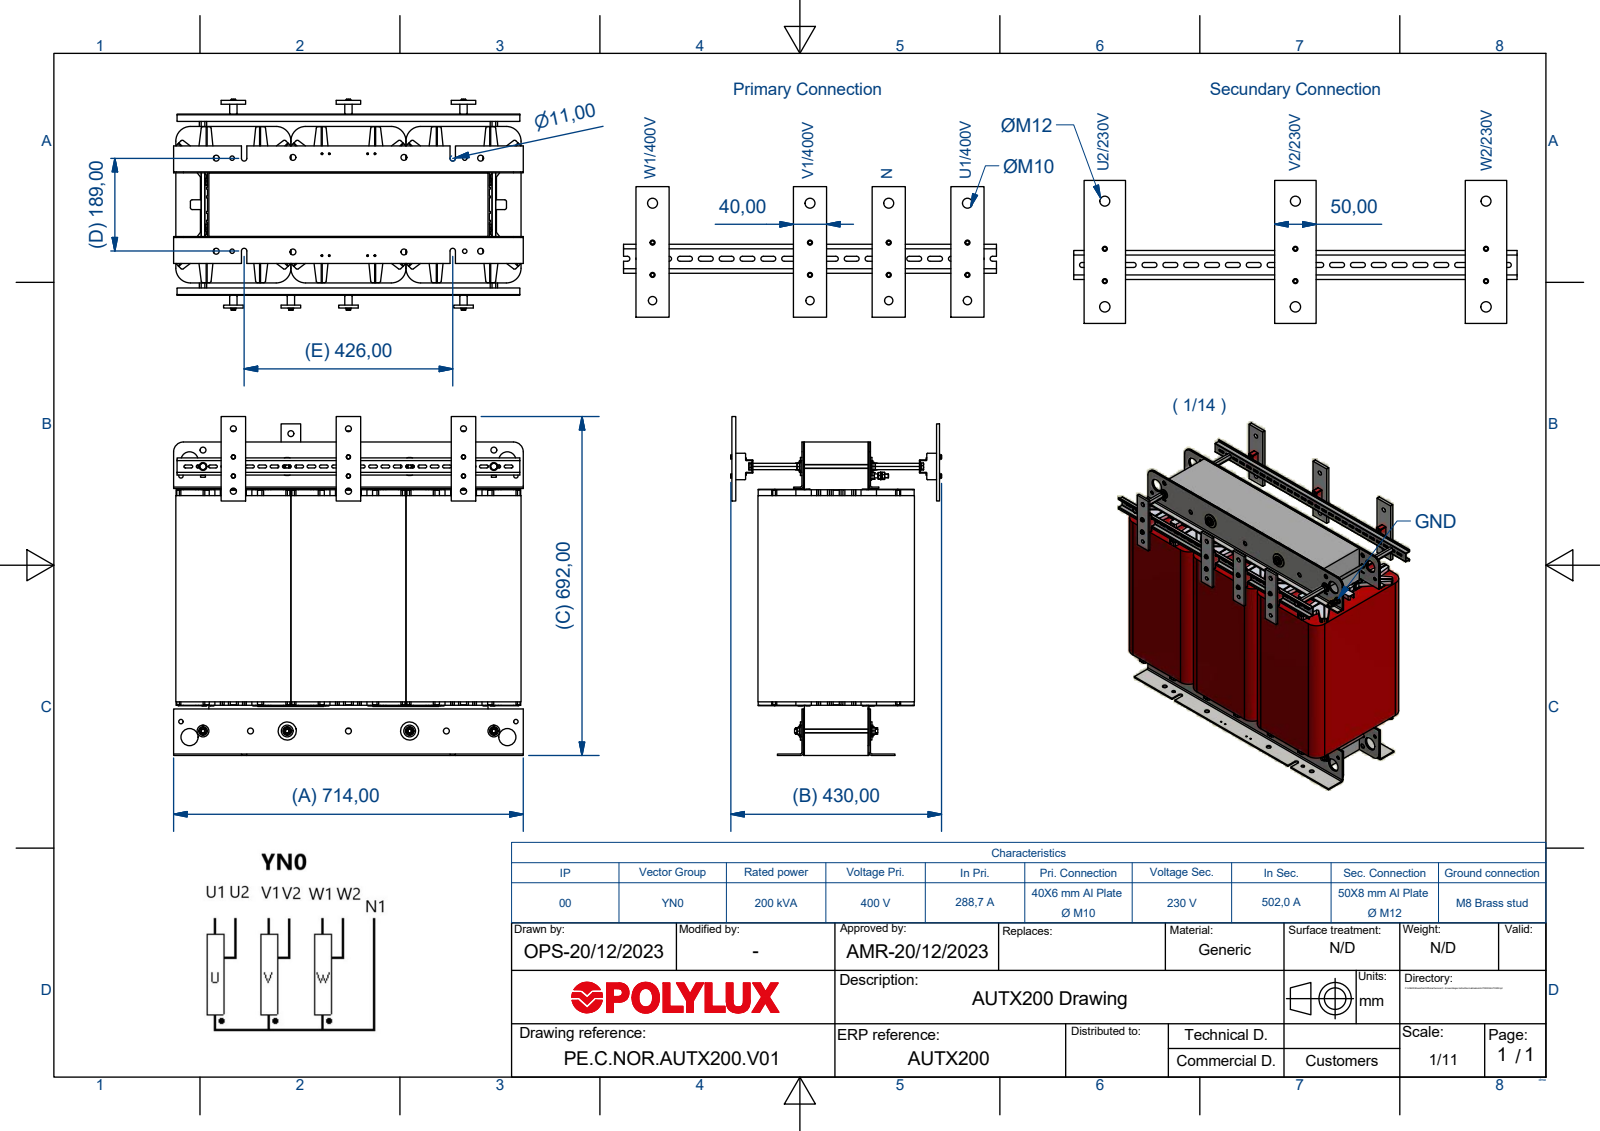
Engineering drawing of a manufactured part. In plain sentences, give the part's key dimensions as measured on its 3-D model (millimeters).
The part is named "AUTX200". Its 3-D file was written by "Autodesk Inventor 2018 (AUTOMOTIVE_DESIGN)". It is 195 solids with 5944 faces: 4187 planar, 1335 cylindrical and 422 other. Overall it measures 714 by 692 by 430.2 millimeters. Its volume is 105 800 000 cubic millimeters and its surface area 6 929 000 square millimeters. Round holes: 33 of diameter 12, 12 of diameter 4.13, 12 of diameter 5, 10 of diameter 11.5, 9 of diameter 6.65, 9 of diameter 8.4, 8 of diameter 3.5, 8 of diameter 6, 8 of diameter 6.4, 8 of diameter 9, 6 of diameter 11.25, 4 of diameter 10. Round bosses or shafts: 9 of diameter 8, 8 of diameter 24, 8 of diameter 12, 8 of diameter 6.88, 4 of diameter 37, 3 of diameter 16, 2 of diameter 11.63, 1 of diameter 12.7. Partial cylindrical surfaces (rounded edges, fillets, slot ends): 116 of radius 0.5, 96 of radius 2, 76 of radius 1, 72 of radius 1.5, 60 of radius 3.5, 58 of radius 3, 48 of radius 1.55, 16 of radius 3.75. The main face-to-face distances are 235, 2, 132, 470, 92.75, 94.75, 224.75, 226.75, 135, 130. The hole center spacings are 540, 250, 15, 30.21, 32.5, 33.5, 34.6, 36.21.
